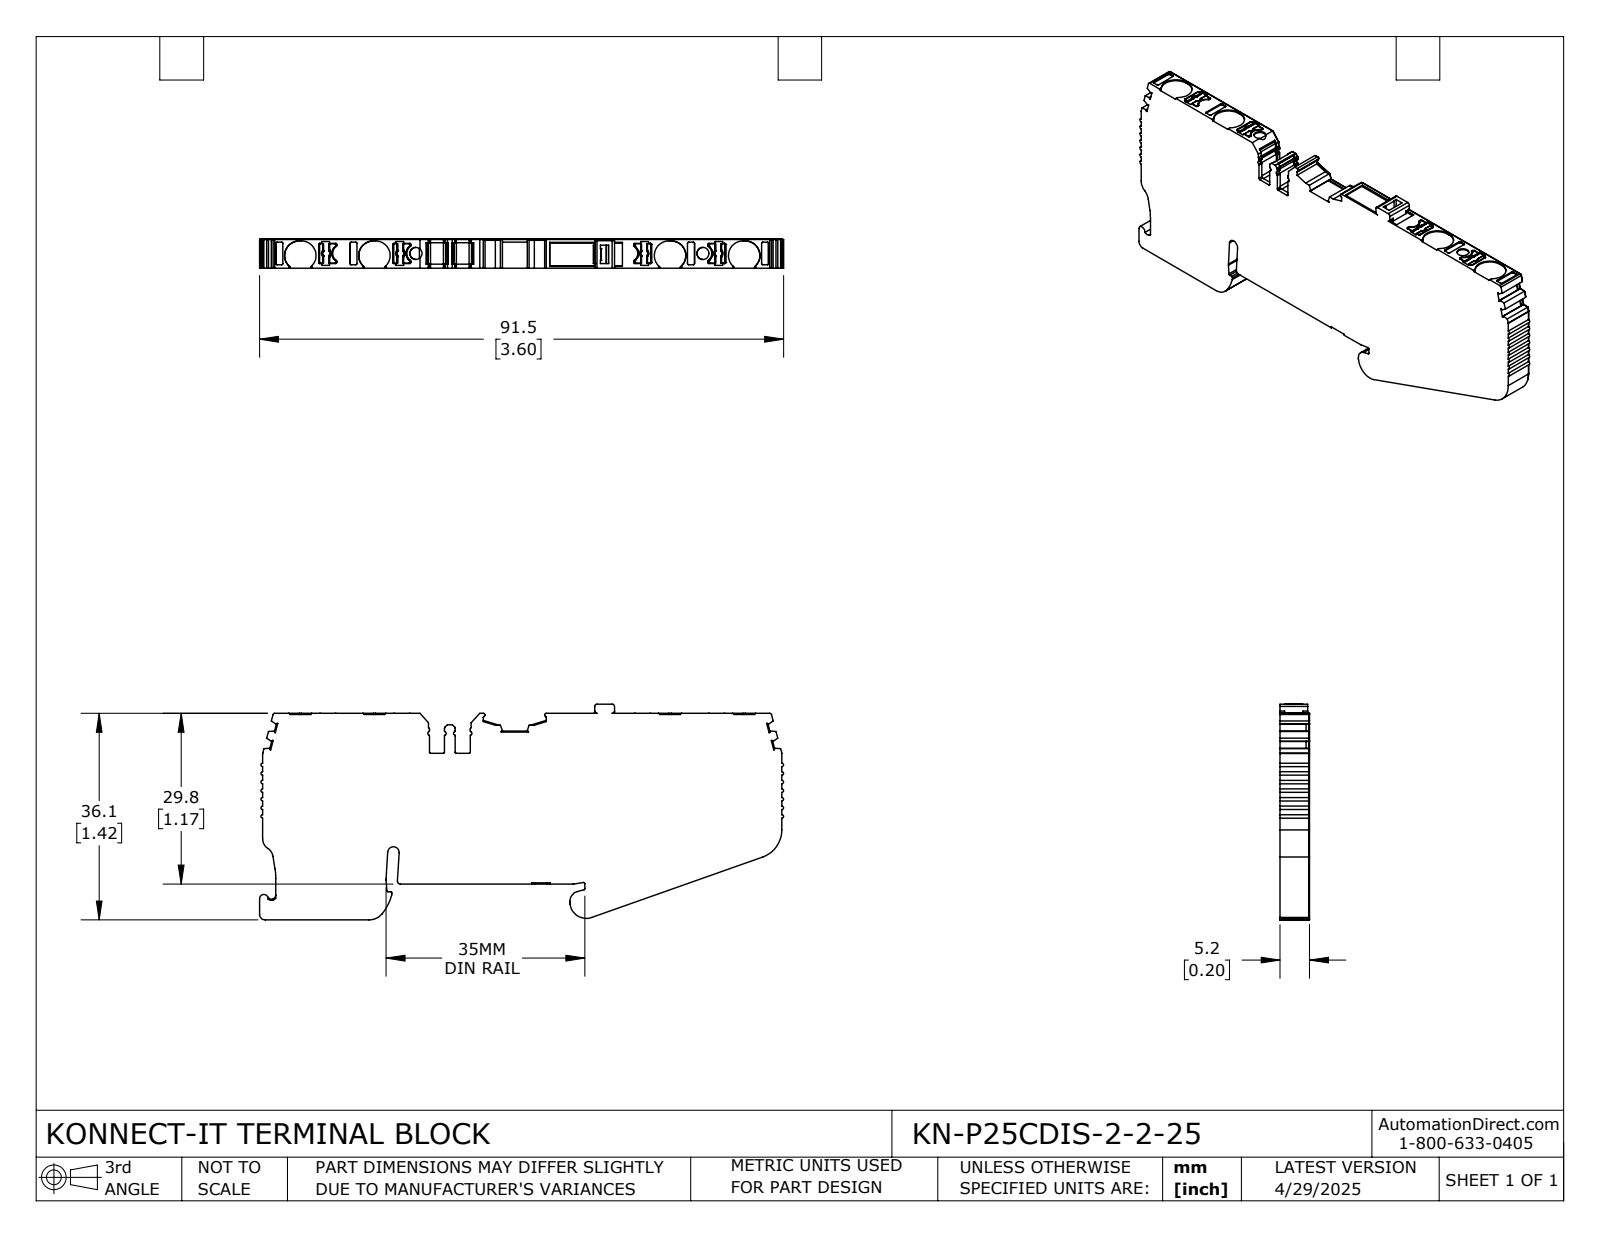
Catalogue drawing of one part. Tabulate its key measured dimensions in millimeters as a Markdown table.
| quantity | value |
| --- | --- |
| part name | KN-P25CDIS-2-2-25 |
| STEP written by | SolidWorks 2024 (CONFIG_CONTROL_DESIGN) |
| units | millimeters |
| bodies | 1 solid, 774 faces (405 planar, 298 cylindrical, 71 other) |
| overall size | 91.5 × 37.7 × 5.2 |
| volume | 14 000 mm³ |
| surface area | 7 194 mm² |
| round holes (diameter × count) | 2.1 × 2 |
| partial cylindrical surfaces (radius × count) | 0.2 × 78, 0.3 × 39, 0.1 × 21, 0.5 × 18, 0.2 × 16, 0.4 × 13, 2.5 × 8, 1 × 4 |
| main face-to-face distances | 5.2, 29.6, 29.8, 6.2, 35.9, 36.1, 90.7, 5, 4.5, 1.2 |
| hole center spacings | 50.1 |
